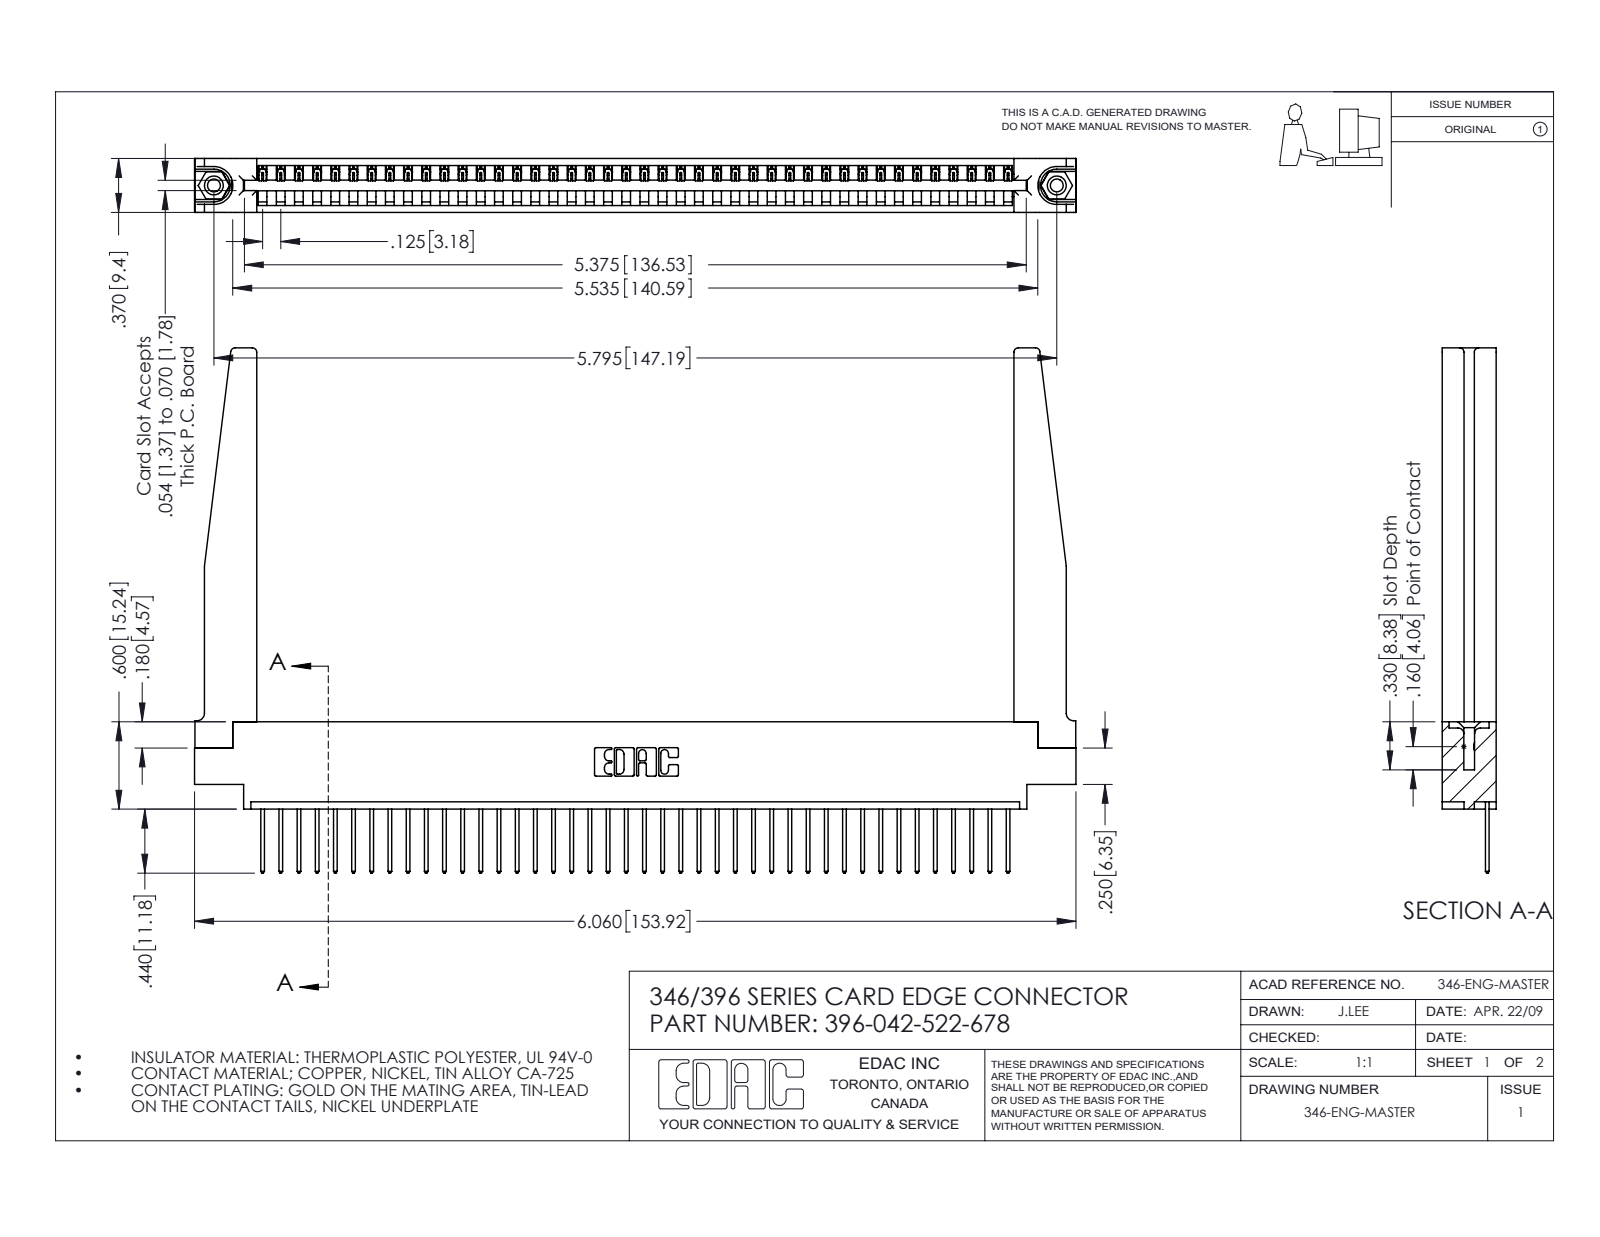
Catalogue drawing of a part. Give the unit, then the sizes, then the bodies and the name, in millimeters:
Units: millimetres
Overall size (bounding box): 153.9 × 91.7 × 9.4
Round holes (diameter × count): ⌀2.3 ×2, ⌀3.2 ×2, ⌀4 ×2, ⌀1.6 ×1
Round bosses / shafts (diameter × count): ⌀3.9 ×2
Partial cylindrical surfaces — rounded edges, fillets, slot ends (radius × count): R0.2 ×84, R0.3 ×84, R0.3 ×22, R0.8 ×8, R0.2 ×6, R0.8 ×6, R0.7 ×3, R0.8 ×2
Main face-to-face distances: 9.4, 1.2, 8.2, 1.8, 3.8, 6.4, 3.8, 7.6, 0.6, 5.6
Hole centre spacings: 6.2, 141.9, 147.2
Volume: 21 500 mm³ · Surface area: 25 080 mm²
Bodies: 47 solids, 2796 faces (1902 planar, 842 cylindrical, 52 other)
Part name (STEP PRODUCT): 346 Part_0.170 Offset - 0.156 Dia-TH; 345-292-001_345-293-122; 396-042-522-678; 345-250-001_345-250-001-102 (+1 more)
STEP written by: SolidWorks 2016 (CONFIG_CONTROL_DESIGN)
